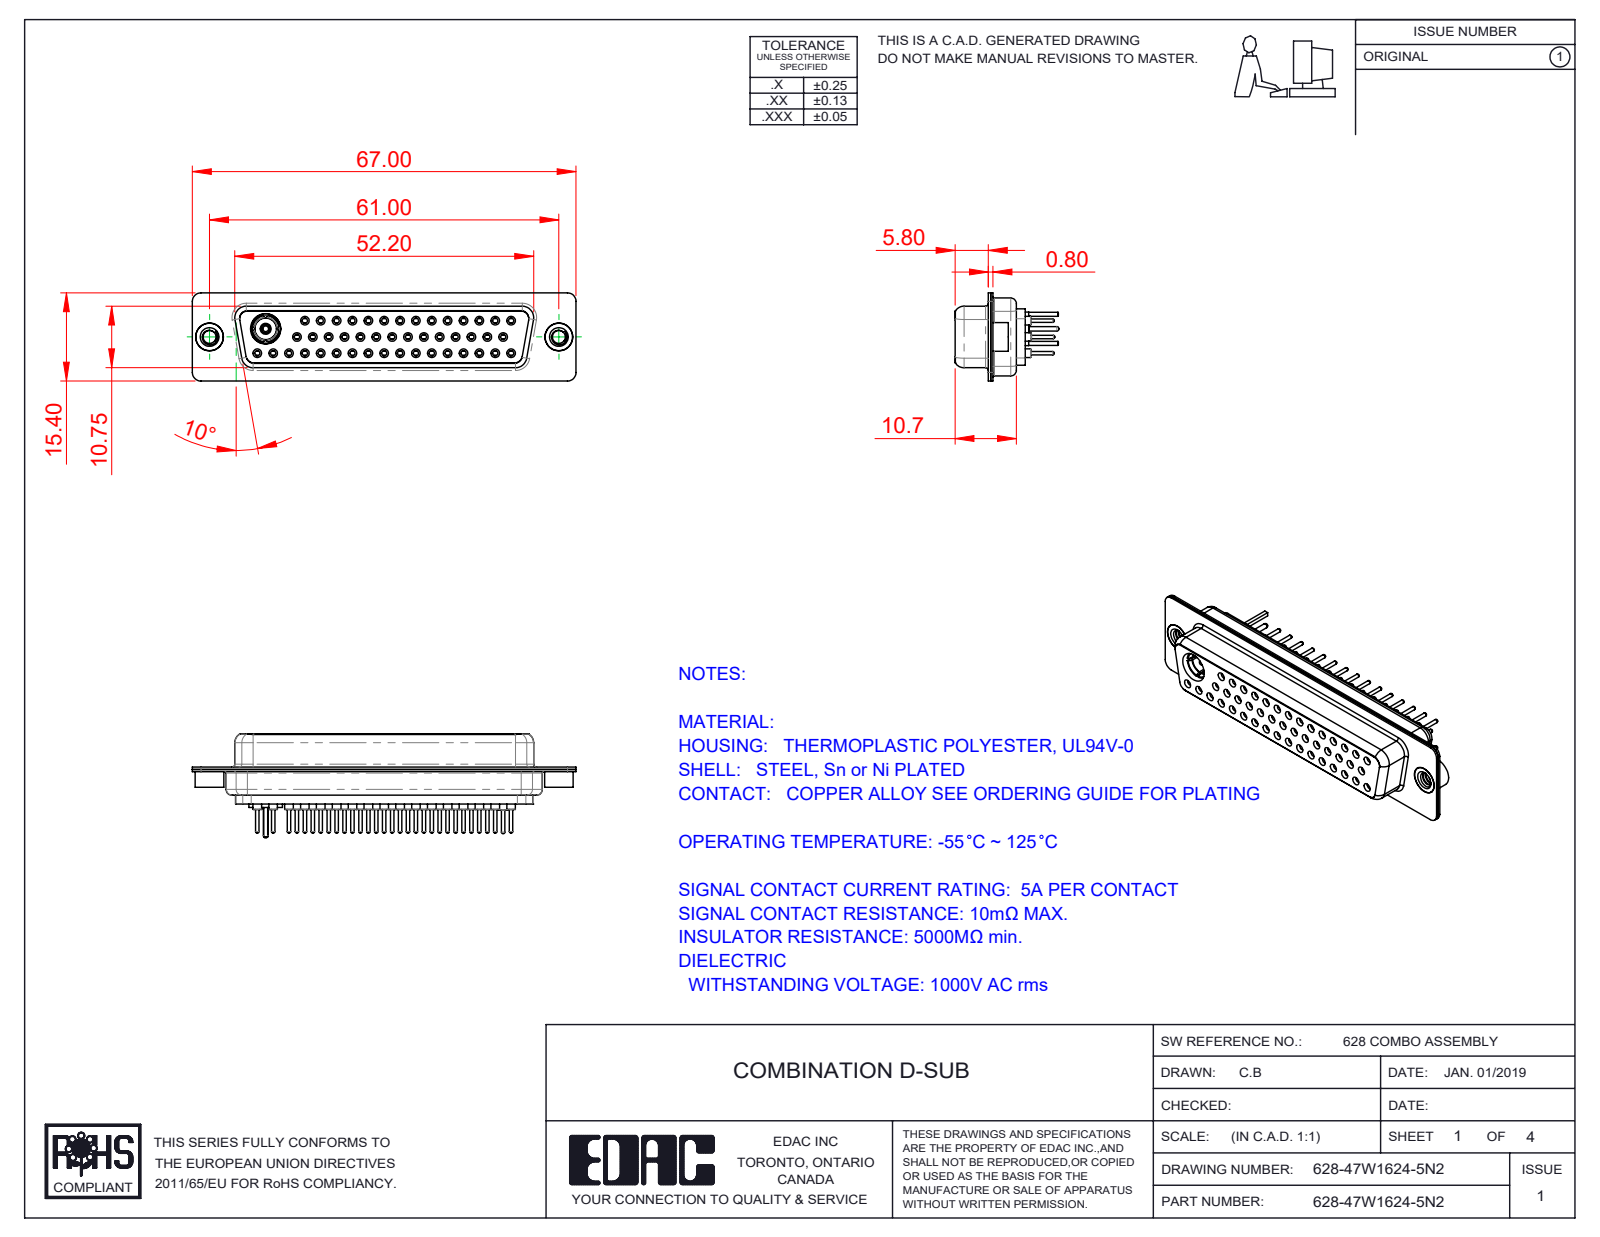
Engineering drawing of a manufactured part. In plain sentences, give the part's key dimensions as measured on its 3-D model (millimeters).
The part is named "628Combo Threaded Rivet_2; Insulator Pin_Straight PC Tail; 628Combo Shell Front_50 Contacts; 628-47W1624-5N2 (+8 more)". Its 3-D file was written by "SolidWorks 2016 (CONFIG_CONTROL_DESIGN)". It is 55 solids with 2923 faces: 811 planar, 1048 cylindrical and 1064 other. Overall it measures 67 by 18.15 by 15.4 millimeters. Its volume is 7 045 cubic millimeters and its surface area 14 880 square millimeters. Round holes: 47 of diameter 1.1, 46 of diameter 1.5, 45 of diameter 0.9, 45 of diameter 2, 31 of diameter 1.6, 14 of diameter 1.7, 3 of diameter 4.85, 2 of diameter 2.26, 2 of diameter 4, 2 of diameter 4.05, 1 of diameter 2.83, 1 of diameter 3.3. Round bosses or shafts: 46 of diameter 2.2, 46 of diameter 0.6, 15 of diameter 1.6, 3 of diameter 5, 2 of diameter 4.95, 2 of diameter 4.8, 1 of diameter 5.85, 1 of diameter 5.2. Partial cylindrical surfaces (rounded edges, fillets, slot ends): 16 of radius 1.5, 12 of radius 1.35, 12 of radius 2, 8 of radius 1.6, 4 of radius 0.25, 4 of radius 0.5, 4 of radius 0.6, 4 of radius 0.65. The main face-to-face distances are 0.4, 6.05, 6.45, 11.33, 1.87, 12.25, 6.2, 5.8, 10.35, 10.93. The hole center spacings are 3.16, 2.77, 5.54, 8.31, 11.08, 13.85, 16.62, 19.39.
